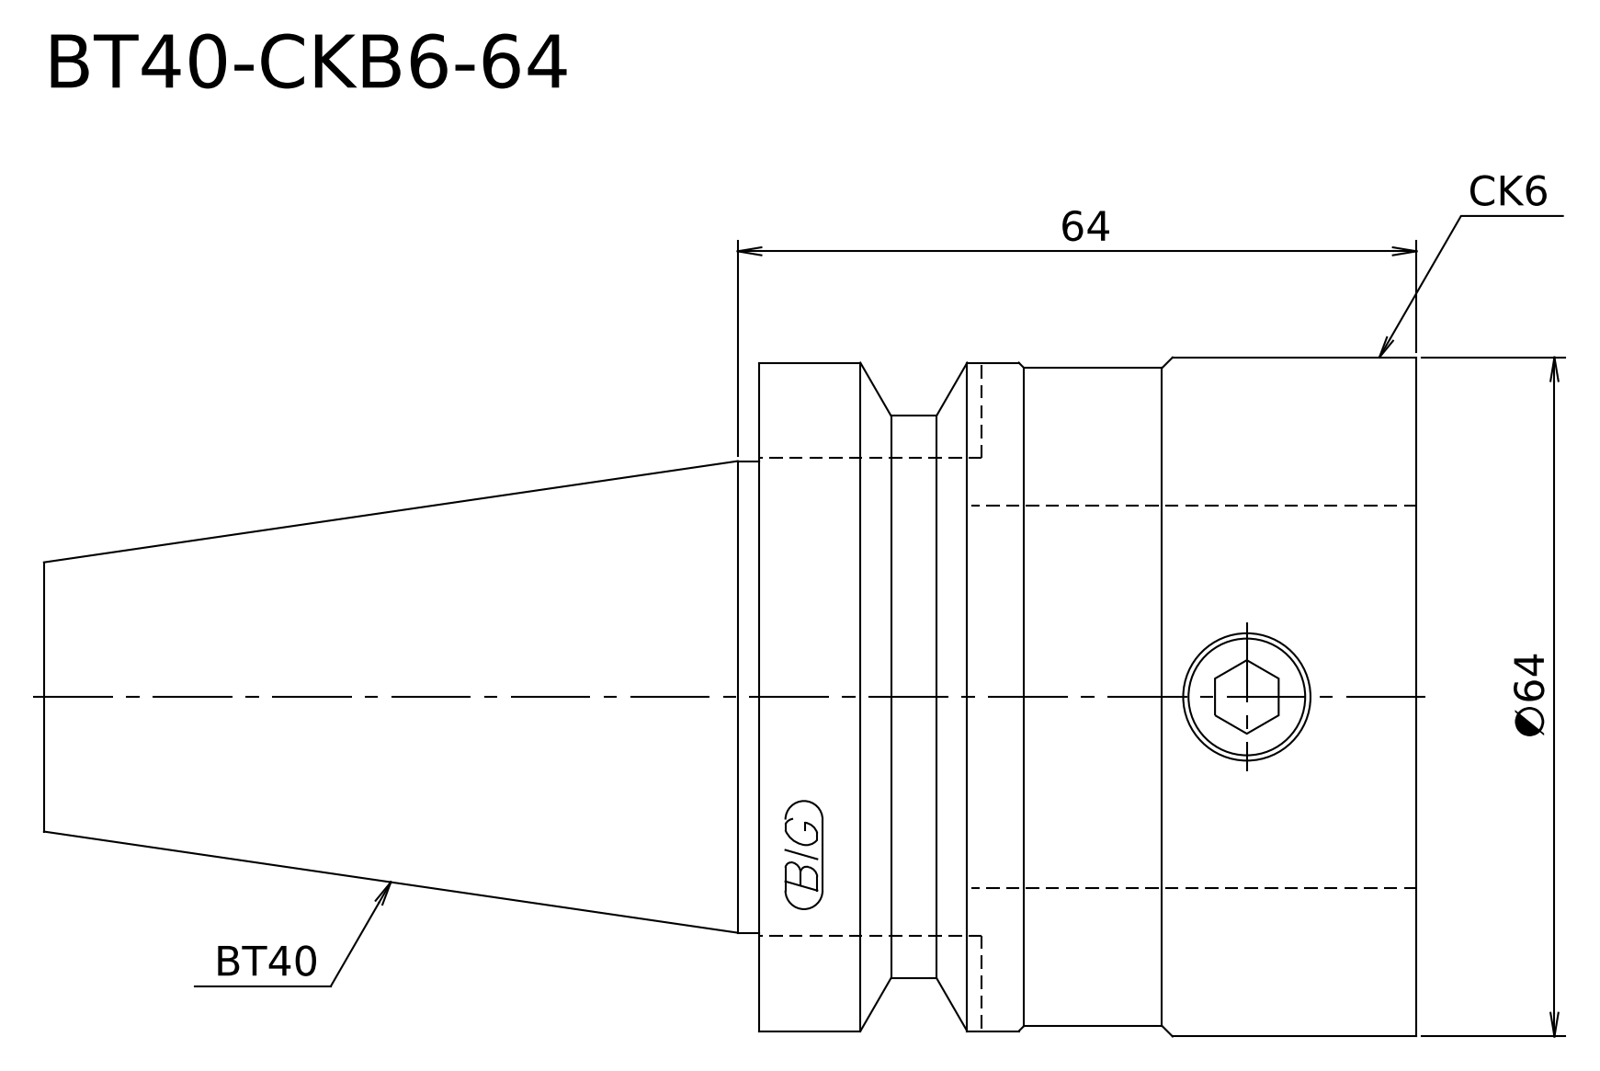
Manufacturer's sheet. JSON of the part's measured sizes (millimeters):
{"step_written_by": "Kubotek KeyCreator V8.5.1 (14335) (CONFIG_CONTROL_DESIGN)", "units": "millimeters", "bodies": {"solids": 1, "faces": 15, "planar": 3, "cylindrical": 6, "other": 6}, "overall_size": [129.4, 64, 64], "volume_mm3": 254876, "surface_area_mm2": 25950, "round_bosses_or_shafts": [[64, 1], [63, 1], [62, 1], [53, 1], [44.45, 1]], "face_to_face_distances": [62, 129.4, 67.4]}
